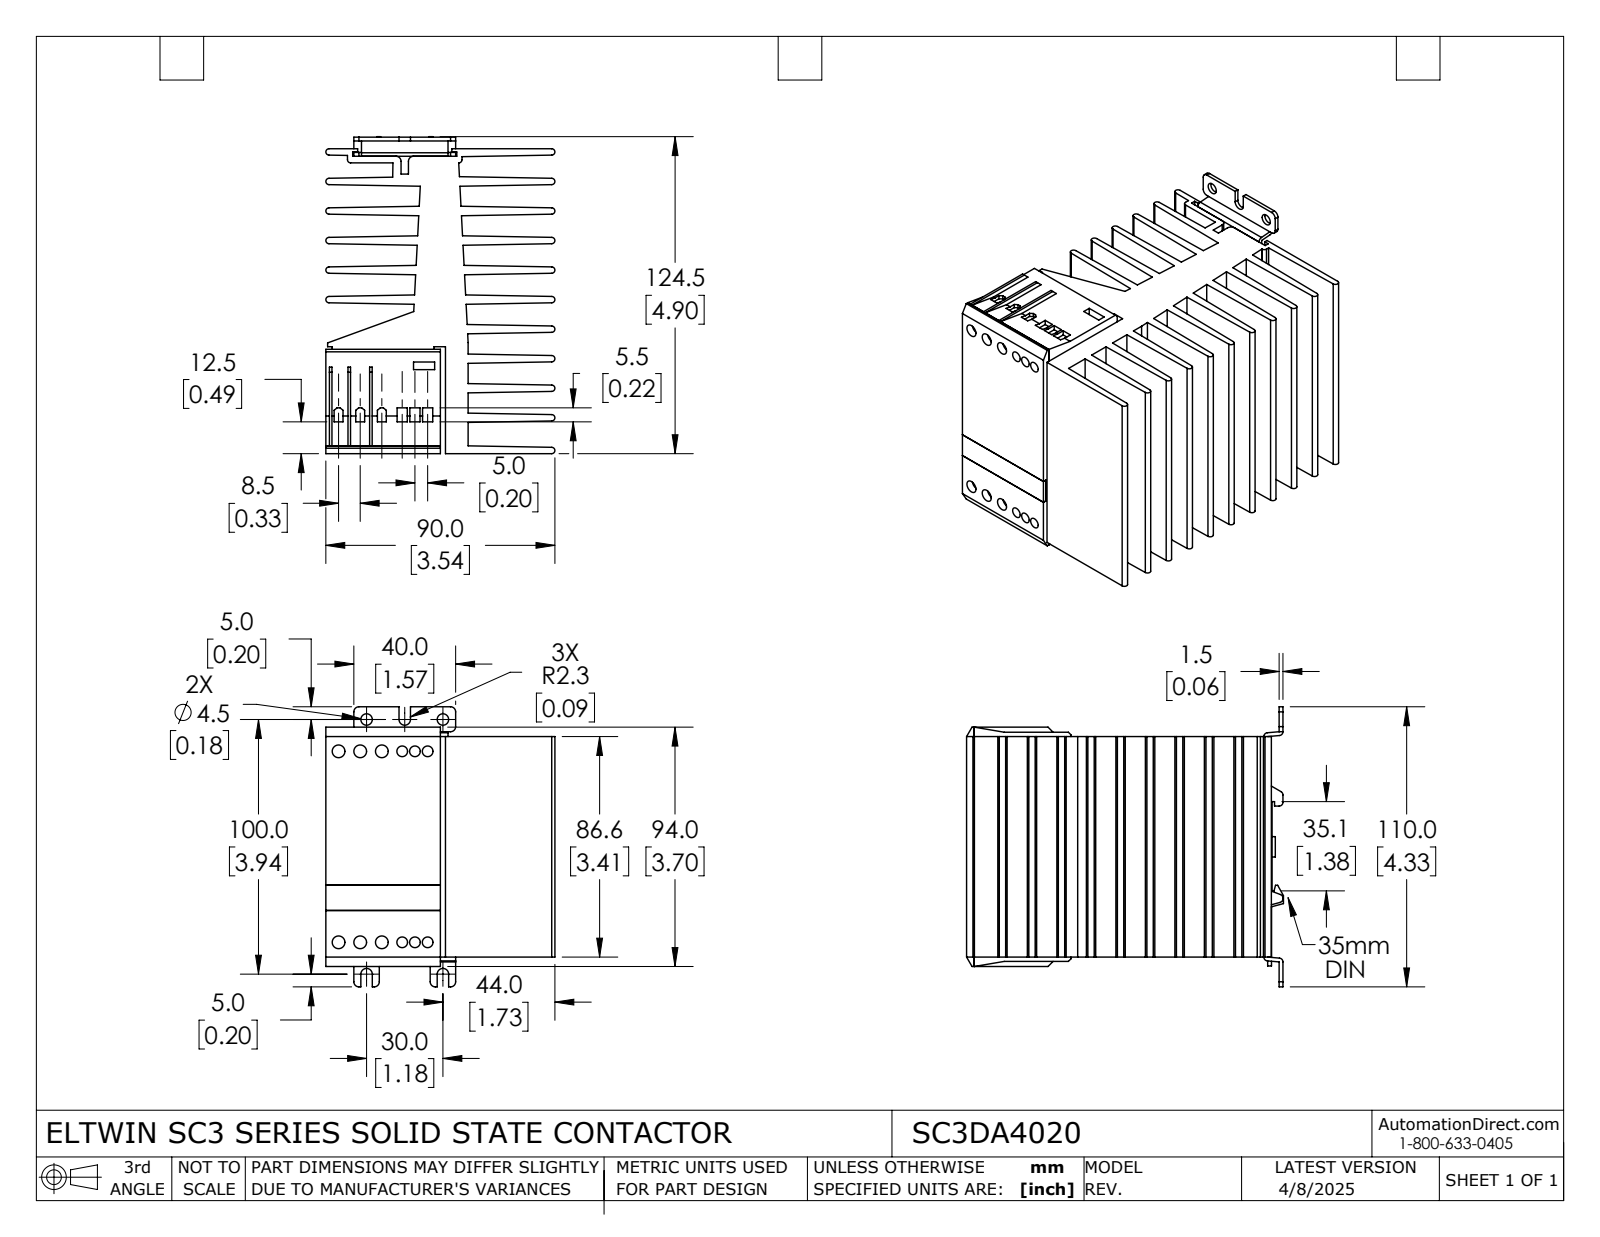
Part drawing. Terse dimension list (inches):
name: SC3DA4020
written by: SolidWorks 2021 (AUTOMOTIVE_DESIGN)
unit: in
bodies: 5 solids, 440 faces (326 planar, 114 cylindrical, 0 other)
size: 4.902 × 4.331 × 3.543
volume: 31.2 in³; area: 277.9 in²
holes: 6× ⌀0.165, 6× ⌀0.173, 6× ⌀0.197, 6× ⌀0.236, 2× ⌀0.177
bosses: 1× ⌀0.315
rounds: 19× R0.049, 18× R0.079, 10× R0.059, 4× R0.051, 3× R0.089
face distances: 0.457, 0.913, 1.37, 0.159, 0.3, 0.157, 1.827, 1.669, 1.828, 2.126
hole spacings: 2.953, 0.197, 0.335, 2.959, 2.972, 1.181, 0.315, 0.394
